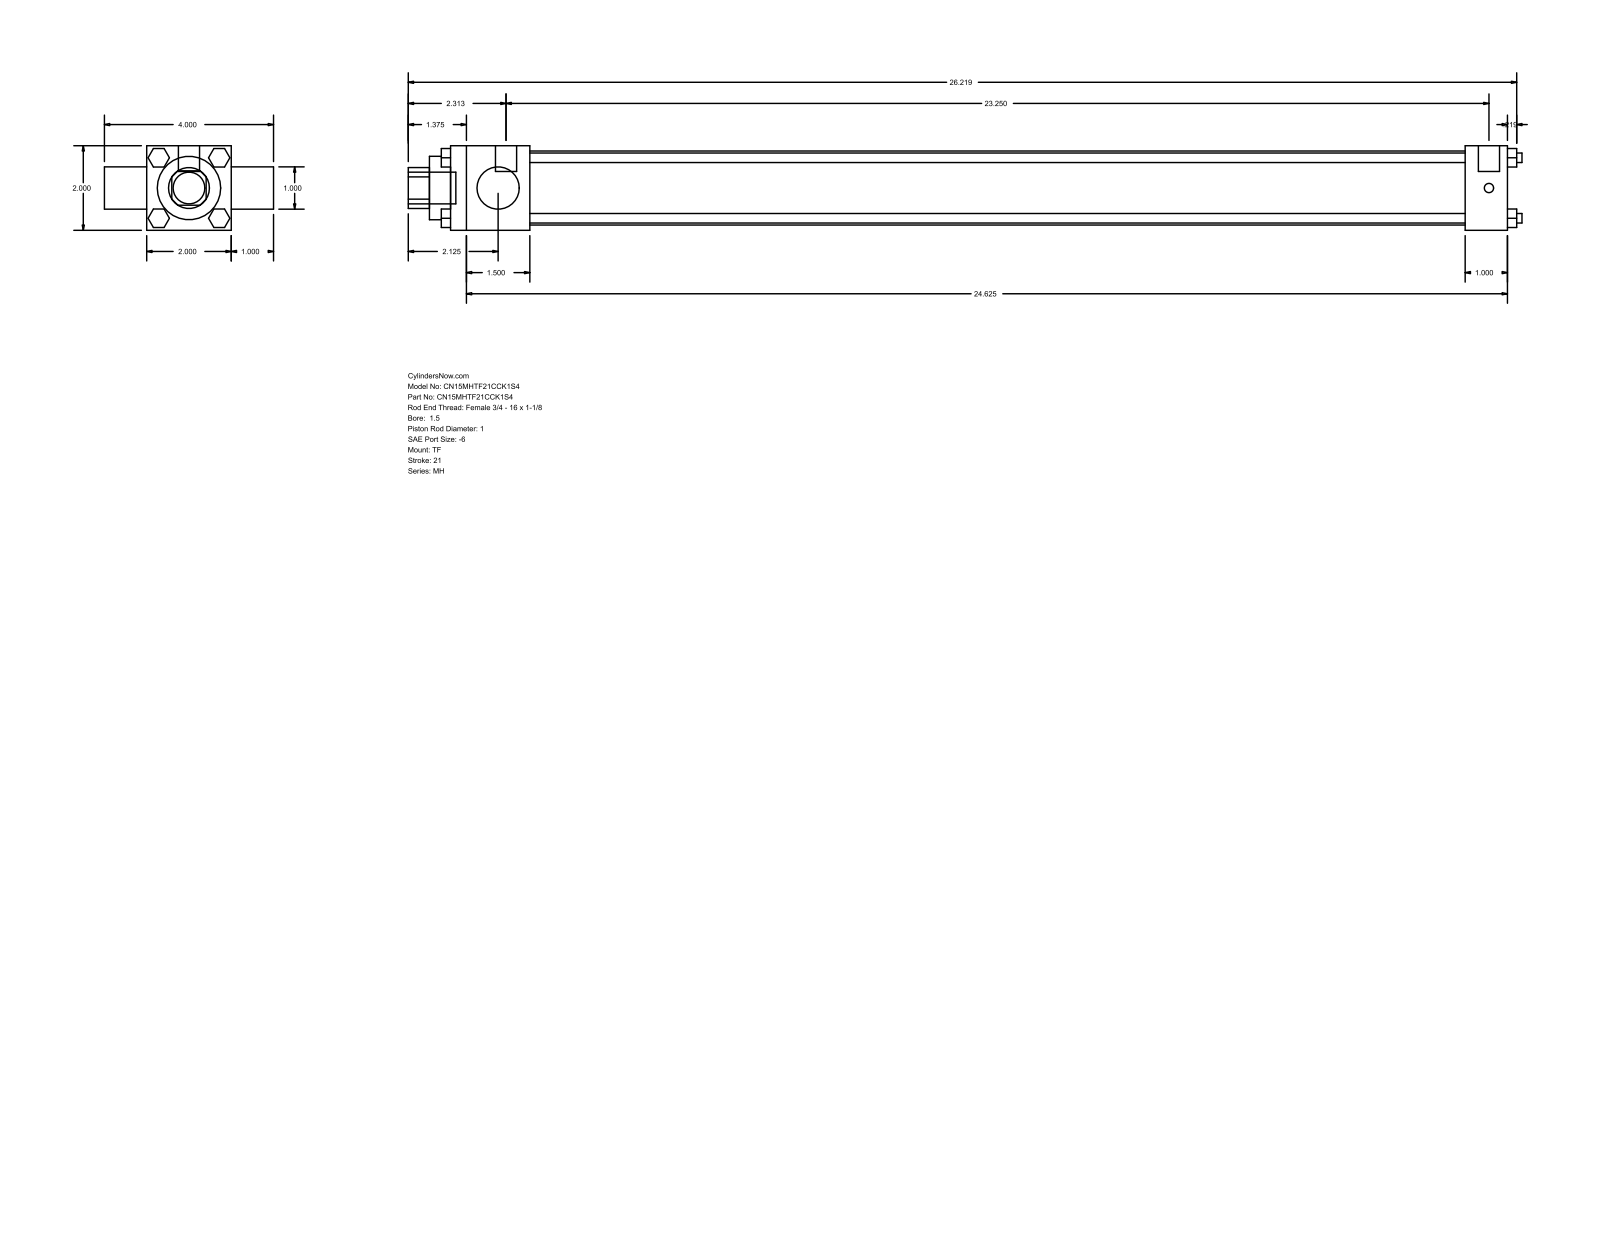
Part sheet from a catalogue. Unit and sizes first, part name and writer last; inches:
Units: inches
Overall size (bounding box): 26.344 × 4 × 2
Round holes (diameter × count): ⌀1 ×2, ⌀1.5 ×1, ⌀1.75 ×1
Round bosses / shafts (diameter × count): ⌀0.225 ×4, ⌀0.219 ×3, ⌀0.5 ×2, ⌀0.75 ×1
Partial cylindrical surfaces — rounded edges, fillets, slot ends (radius × count): R0.484 ×1
Main face-to-face distances: 2, 1, 25, 3, 1.875, 23.125, 24, 22.125, 25.219, 0.5
Bodies: 0 solids, 120 faces (92 planar, 28 cylindrical, 0 other)
Part name (STEP PRODUCT): MH_TF__0150_1
STEP written by: GSSL Pune (CONFIG_CONTROL_DESIGN)
